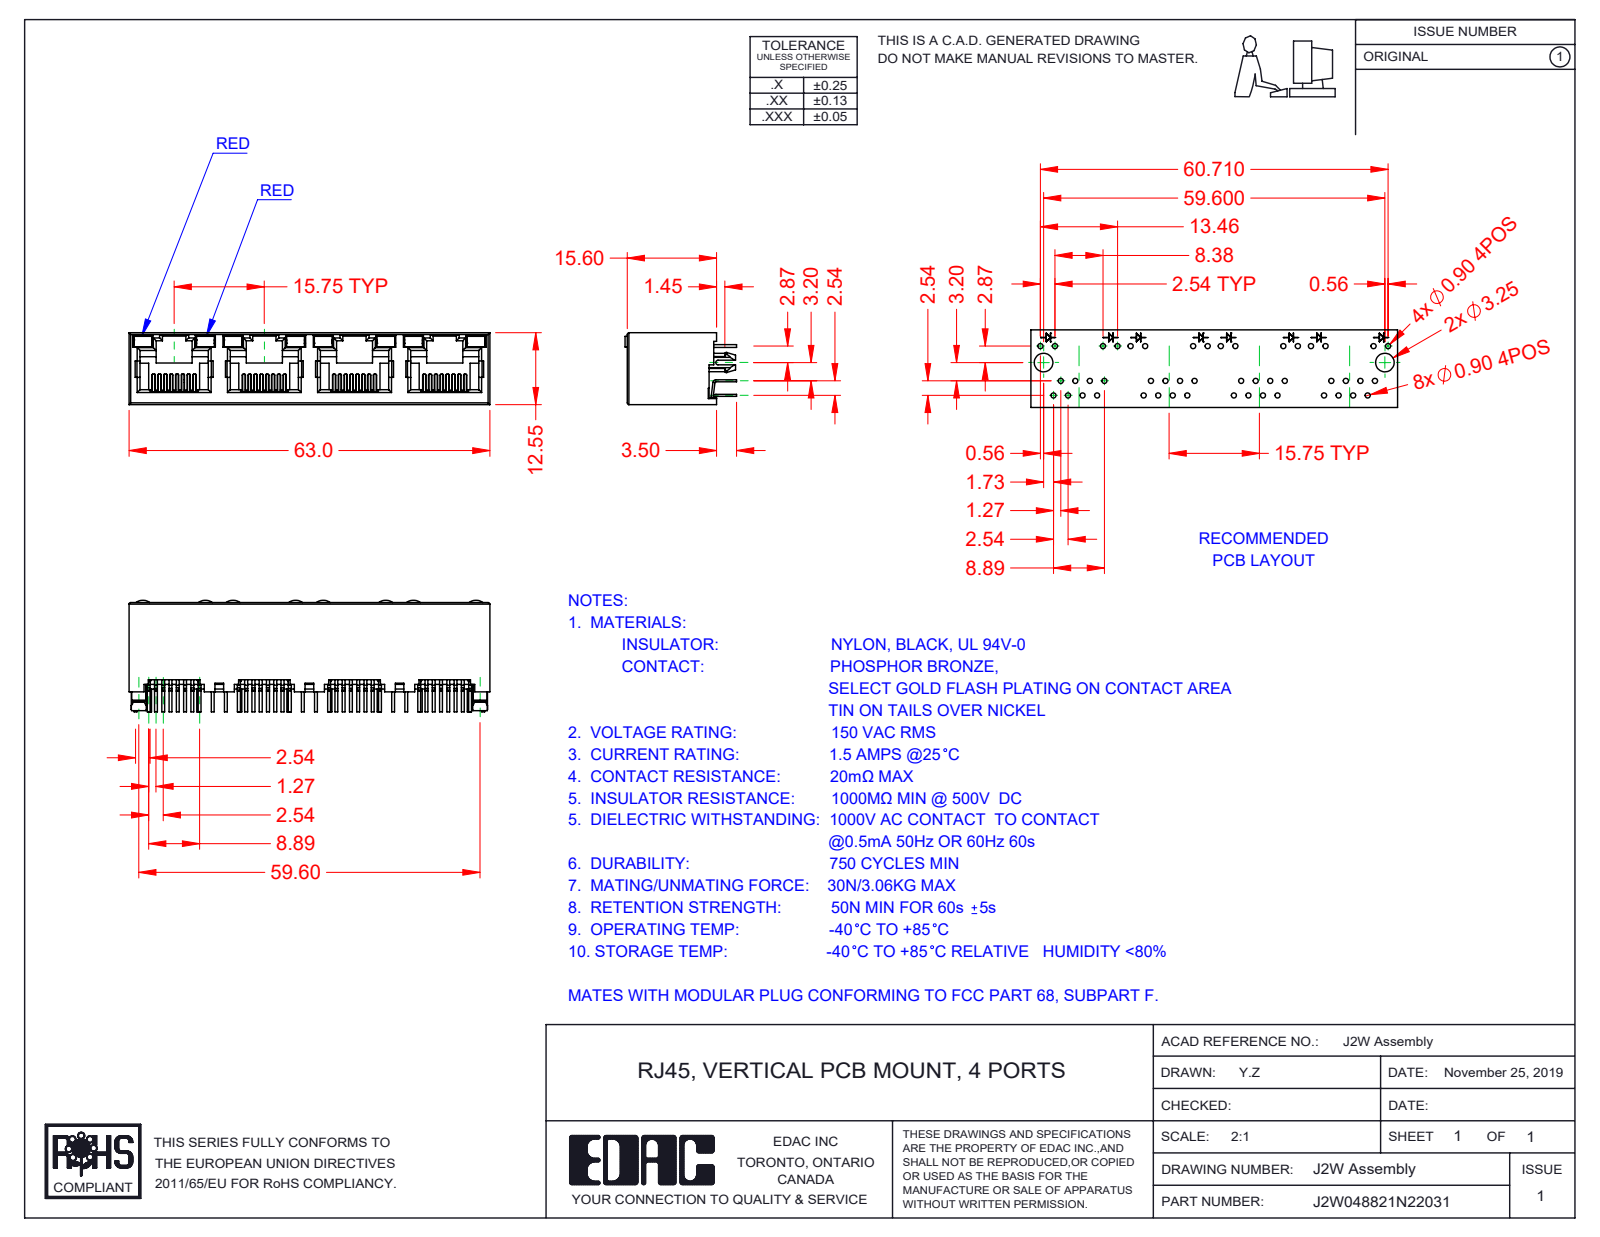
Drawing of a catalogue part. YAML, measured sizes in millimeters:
part_name: "2W Contacts; J2W048821N22031; 2W LED RH_2-Red; 2W LED LH_2-Red (+2 more)"
step_written_by: "SolidWorks 2020 (CONFIG_CONTROL_DESIGN)"
units: millimeters
bodies: {solids: 45, faces: 3135, planar: 2600, cylindrical: 477, other: 58}
overall_size: [63, 19.5, 12.55]
volume: 5335
surface_area: 13144
partial_cylinders:
  - {radius: 0.15, count: 64}
  - {radius: 0.2, count: 29}
  - {radius: 0.5, count: 28}
  - {radius: 0.3, count: 14}
  - {radius: 0.45, count: 8}
  - {radius: 2, count: 8}
  - {radius: 0.25, count: 2}
  - {radius: 1.5, count: 2}
face_to_face_distances: [12.55, 11.9, 0.65, 15.75, 0.36, 1.5, 0.78, 0.6, 11.3, 31.5]
